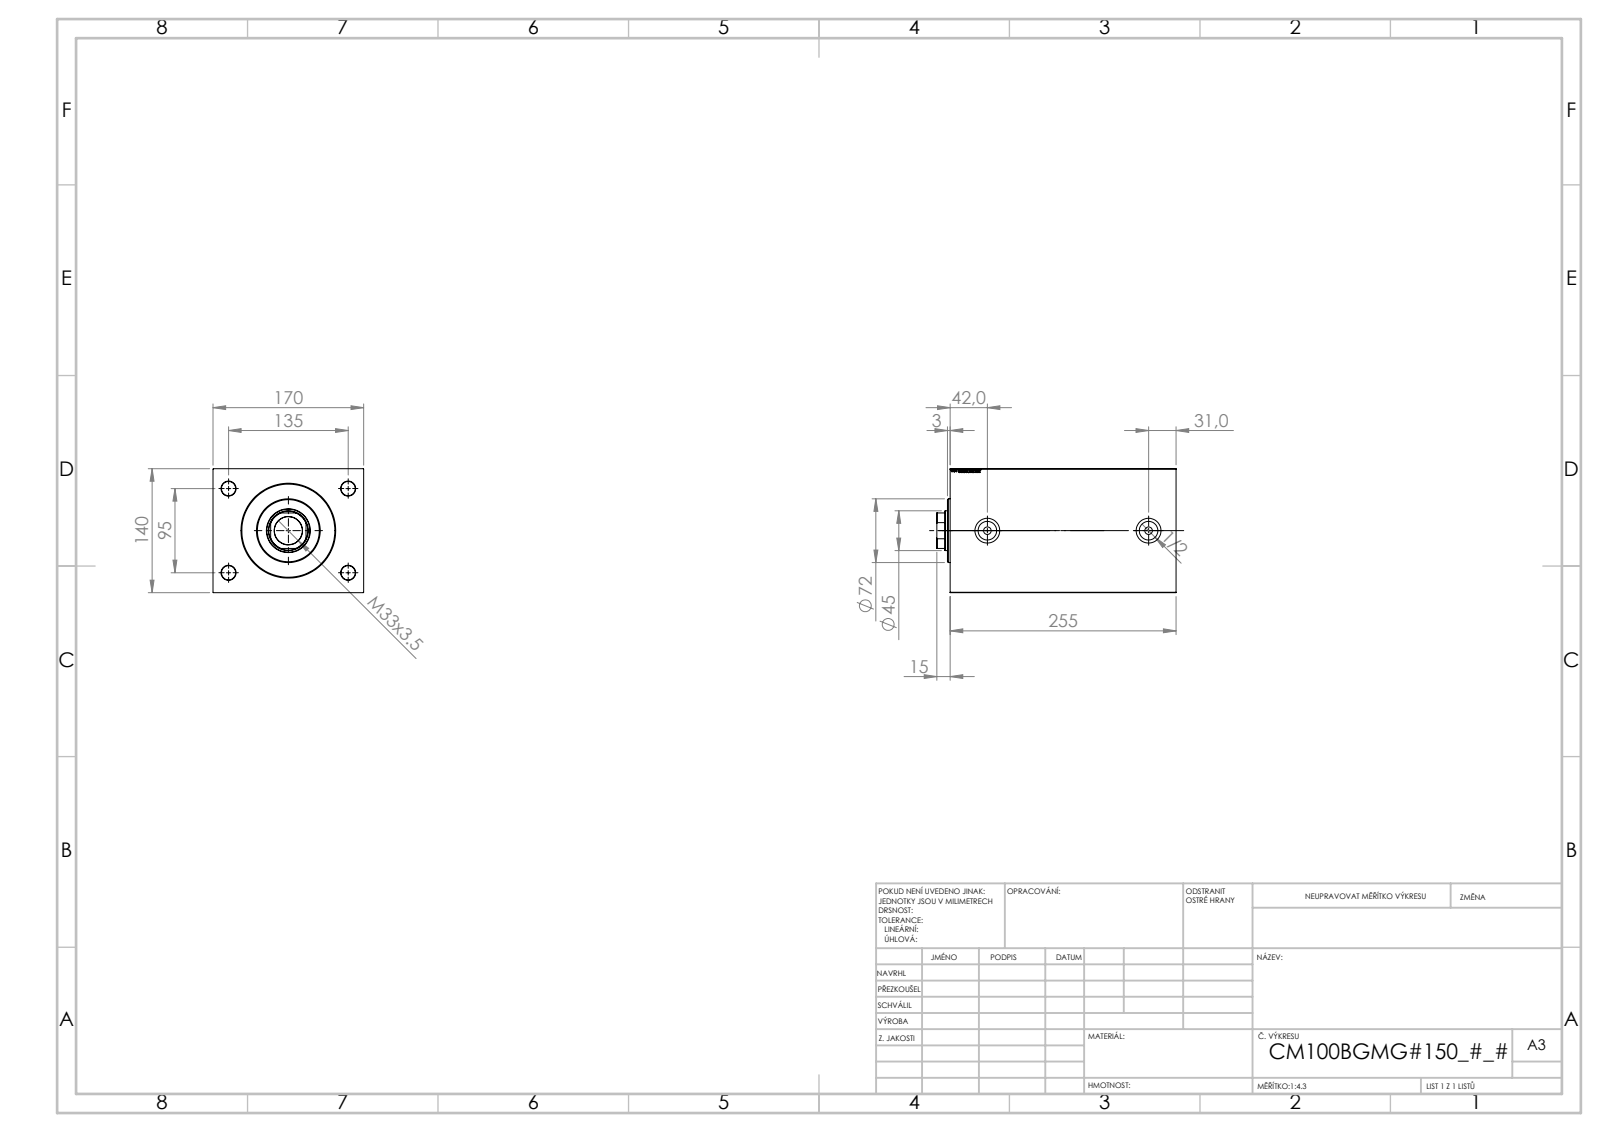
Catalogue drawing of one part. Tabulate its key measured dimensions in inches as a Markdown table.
| quantity | value |
| --- | --- |
| part name | V450CM_B_Body; V450CM_VC_B; V450CM_B_VCP |
| STEP written by | SolidWorks 2019 (CONFIG_CONTROL_DESIGN) |
| units | inches |
| bodies | 3 solids, 884 faces (402 planar, 56 cylindrical, 426 other) |
| overall size | 10.63 × 6.693 × 5.512 |
| volume | 309 in³ |
| surface area | 588.2 in² |
| round holes (diameter × count) | 0.63 × 4, 0.335 × 2, 0.825 × 2, 1.102 × 2, 1.24 × 1, 1.772 × 1, 1.909 × 1, 1.949 × 1, 3.937 × 1, 4.016 × 1, 4.134 × 1 |
| round bosses / shafts (diameter × count) | 2.835 × 1 |
| partial cylindrical surfaces (radius × count) | 0.866 × 1 |
| main face-to-face distances | 5.512, 6.693, 10.039, 9.016, 1.024, 0.591, 8.425, 9.449, 3.543, 2.52 |
| hole center spacings | 3.25, 3.74, 5.315, 6.499, 7.165 |
